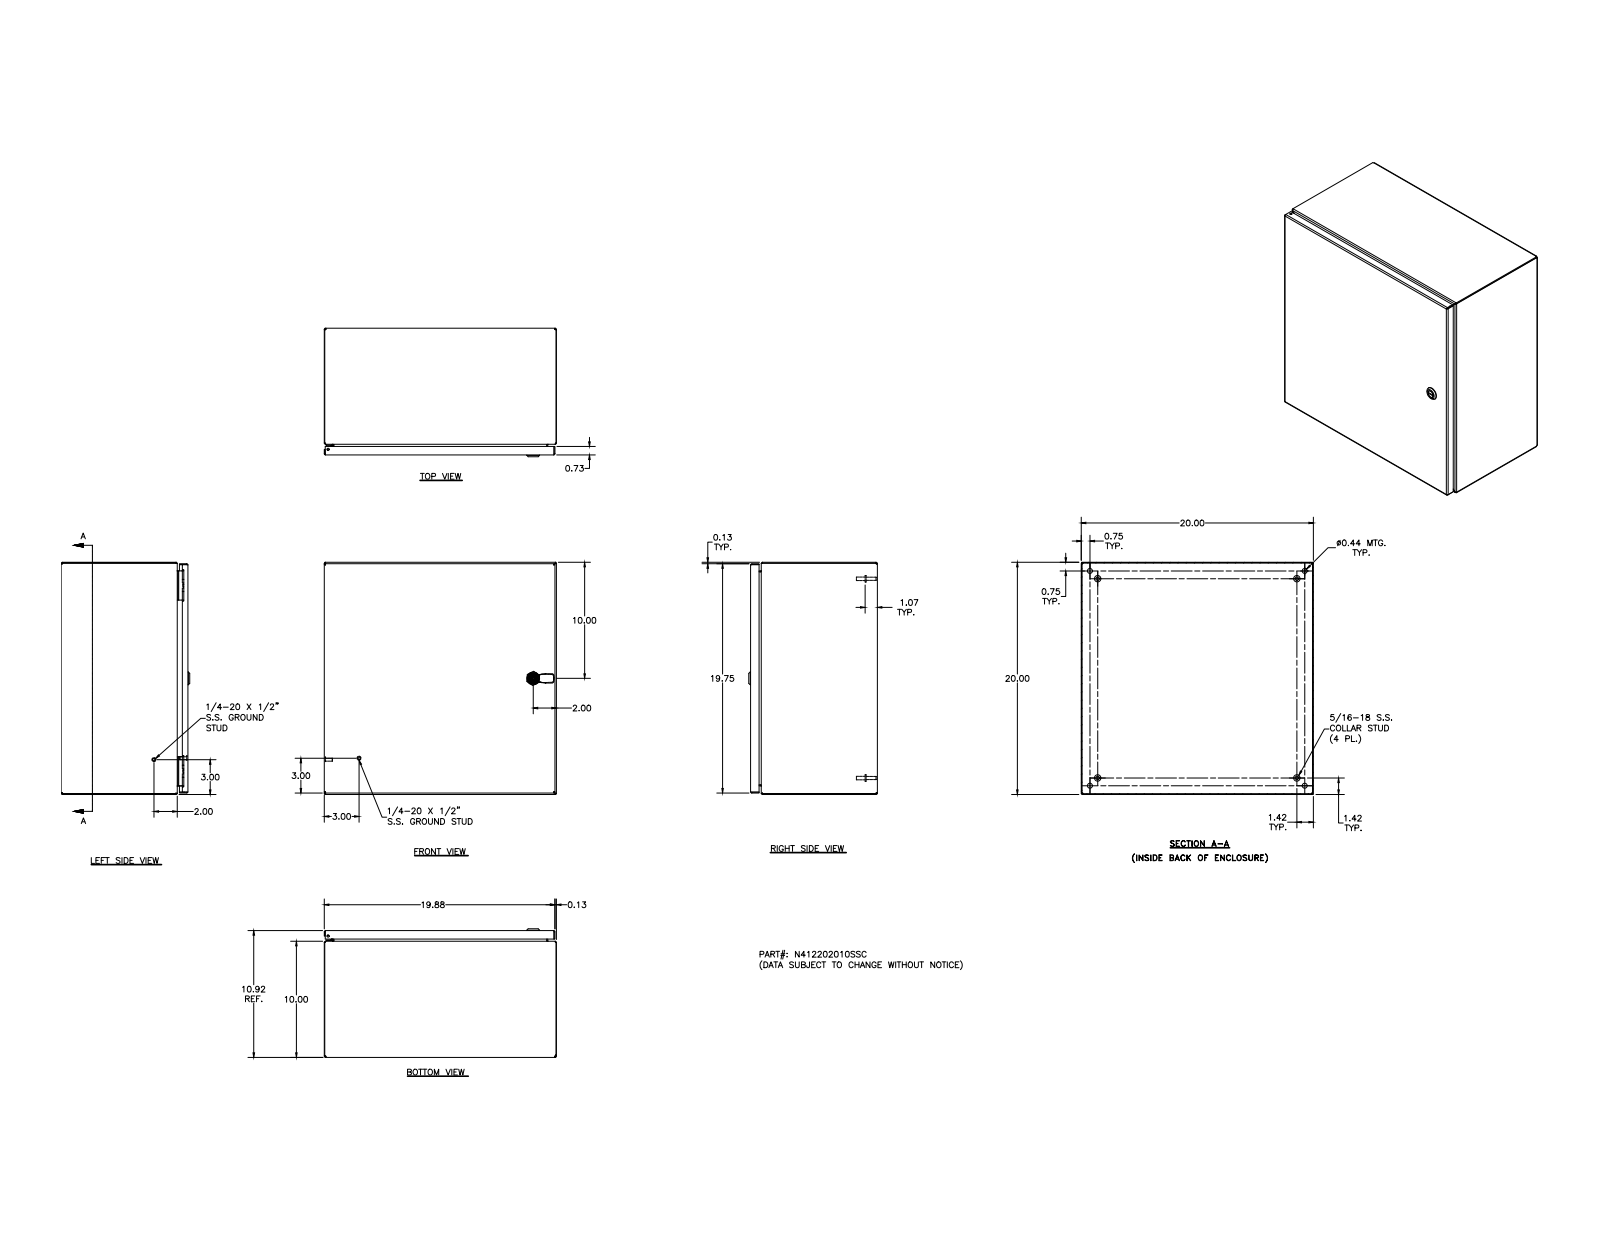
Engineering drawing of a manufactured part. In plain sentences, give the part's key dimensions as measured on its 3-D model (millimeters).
The part is named "N412202010SSC; N412202010SSCBKP; 388151; N4122020SSCLID (+8 more)". Its 3-D file was written by "Autodesk Inventor 2011 (AUTOMOTIVE_DESIGN)". It is 34 solids with 1384 faces: 531 planar, 509 cylindrical and 344 other. Overall it measures 508 by 508 by 281.3 millimeters. Its volume is 2 137 000 cubic millimeters and its surface area 2 287 000 square millimeters. Round holes: 5 of diameter 4.8, 4 of diameter 2.4, 4 of diameter 3.9, 4 of diameter 4.2, 4 of diameter 4.4, 4 of diameter 11.1, 2 of diameter 4, 1 of diameter 4.7, 1 of diameter 5, 1 of diameter 8, 1 of diameter 10, 1 of diameter 10.2. Round bosses or shafts: 10 of diameter 6.4, 4 of diameter 14.3, 4 of diameter 9.1, 4 of diameter 8.1, 4 of diameter 7.6, 4 of diameter 7, 4 of diameter 6.5, 4 of diameter 4.2. Partial cylindrical surfaces (rounded edges, fillets, slot ends): 30 of radius 0.8, 26 of radius 1.3, 20 of radius 2.7, 18 of radius 0.4, 14 of radius 3.2, 9 of radius 0.5, 8 of radius 0.8, 8 of radius 1.8. The main face-to-face distances are 1.9, 506.1, 275.4, 504.2, 508, 273.5, 277.3, 252.1, 23.3, 18.8. The hole center spacings are 406.4, 0.4, 16.8, 406.6, 469.9, 479.3, 0.5, 12.7.
